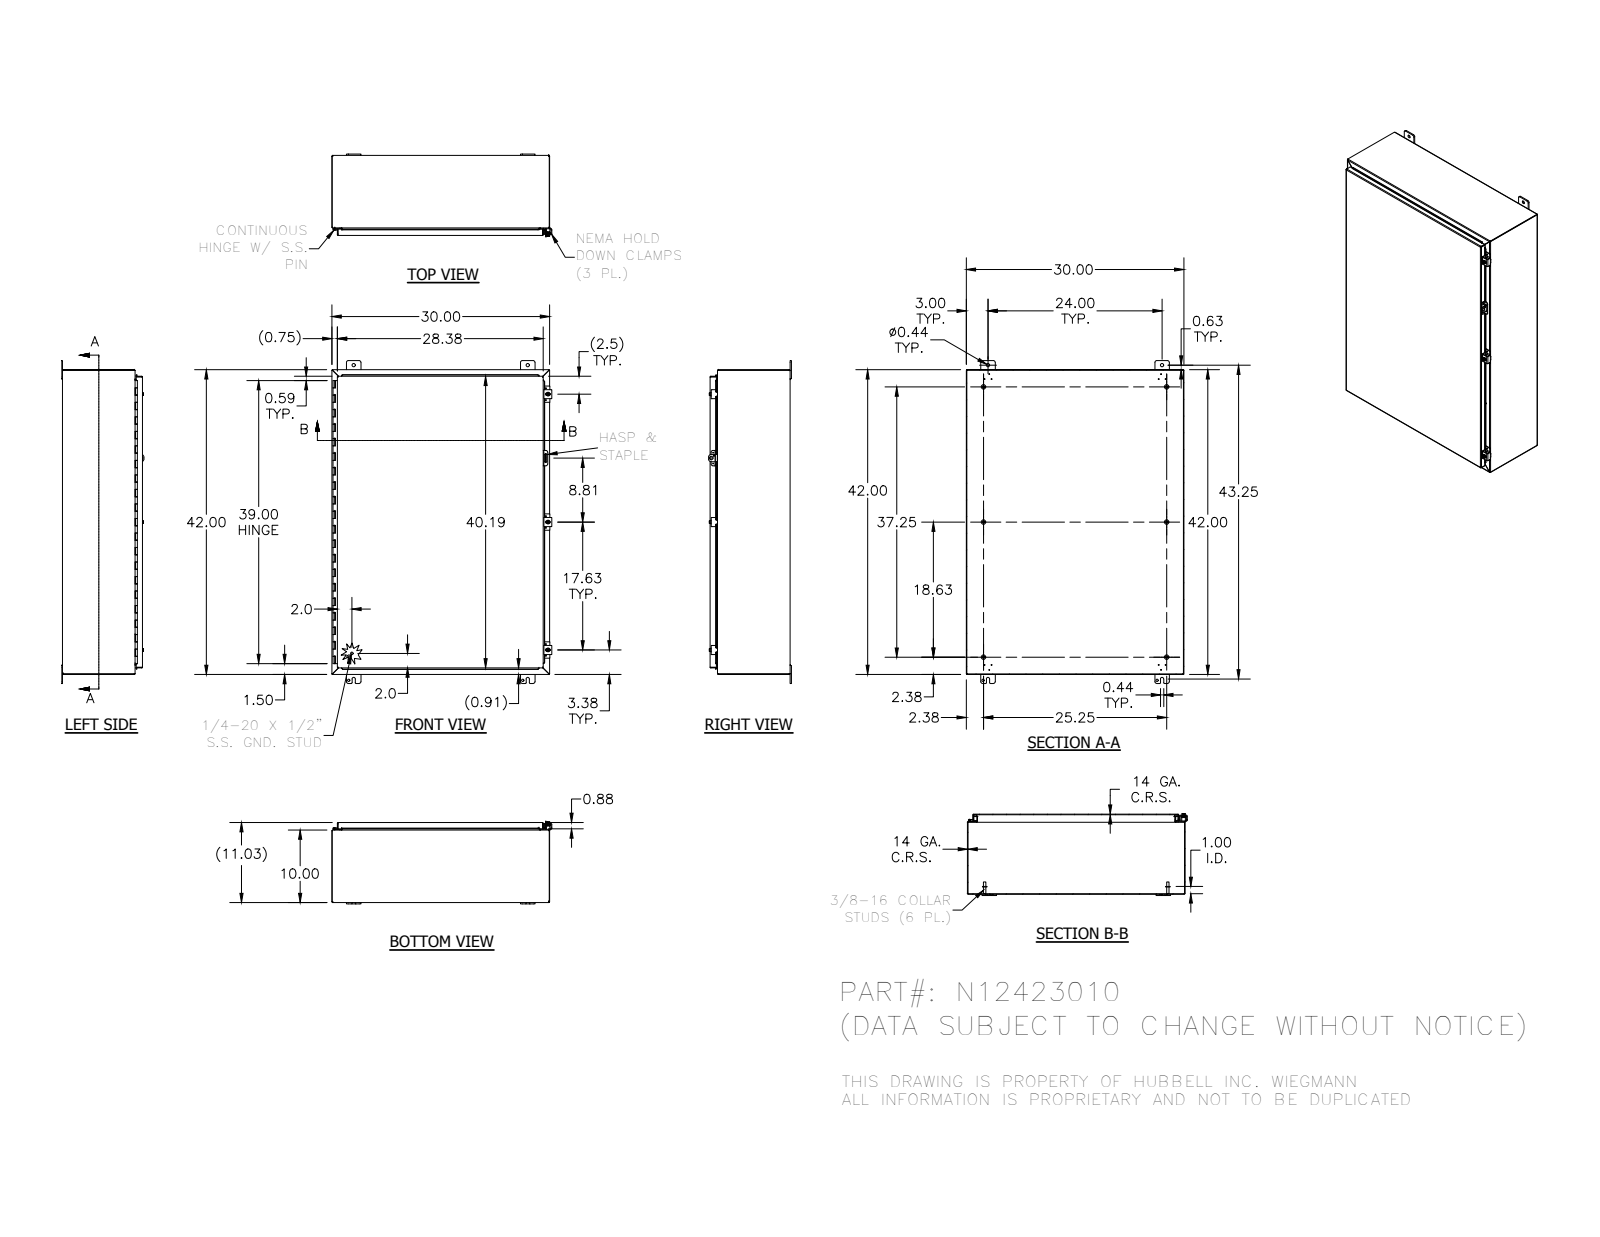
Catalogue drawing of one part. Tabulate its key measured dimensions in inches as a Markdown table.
| quantity | value |
| --- | --- |
| part name | N12423010; 34840; 38420; N12423010BKP (+8 more) |
| STEP written by | Autodesk Inventor 2012 (AUTOMOTIVE_DESIGN) |
| units | inches |
| bodies | 34 solids, 1288 faces (707 planar, 438 cylindrical, 143 other) |
| overall size | 44.5 × 30.311 × 11.41 |
| volume | 340.9 in³ |
| surface area | 8 999 in² |
| round holes (diameter × count) | 0.12 × 12, 0.11 × 9, 0.313 × 4, 0.438 × 4, 0.211 × 3, 0.281 × 3, 0.3 × 3, 0.125 × 1, 0.156 × 1, 0.5 × 1 |
| round bosses / shafts (diameter × count) | 0.625 × 6, 0.33 × 6, 0.25 × 5, 0.52 × 3, 0.5 × 3, 0.35 × 3, 0.115 × 2, 0.337 × 1 |
| partial cylindrical surfaces (radius × count) | 0.03 × 39, 0.063 × 31, 0.125 × 27, 0.25 × 27, 0.031 × 23, 0.105 × 23, 0.07 × 8, 0.1 × 6 |
| main face-to-face distances | 0.074, 10.959, 10.885, 11.033, 29.926, 41.926, 29.852, 30, 9.926, 1.033 |
| hole center spacings | 24, 0.759, 0.839, 0.876, 0.94, 0.969, 1.995, 23.367 |
